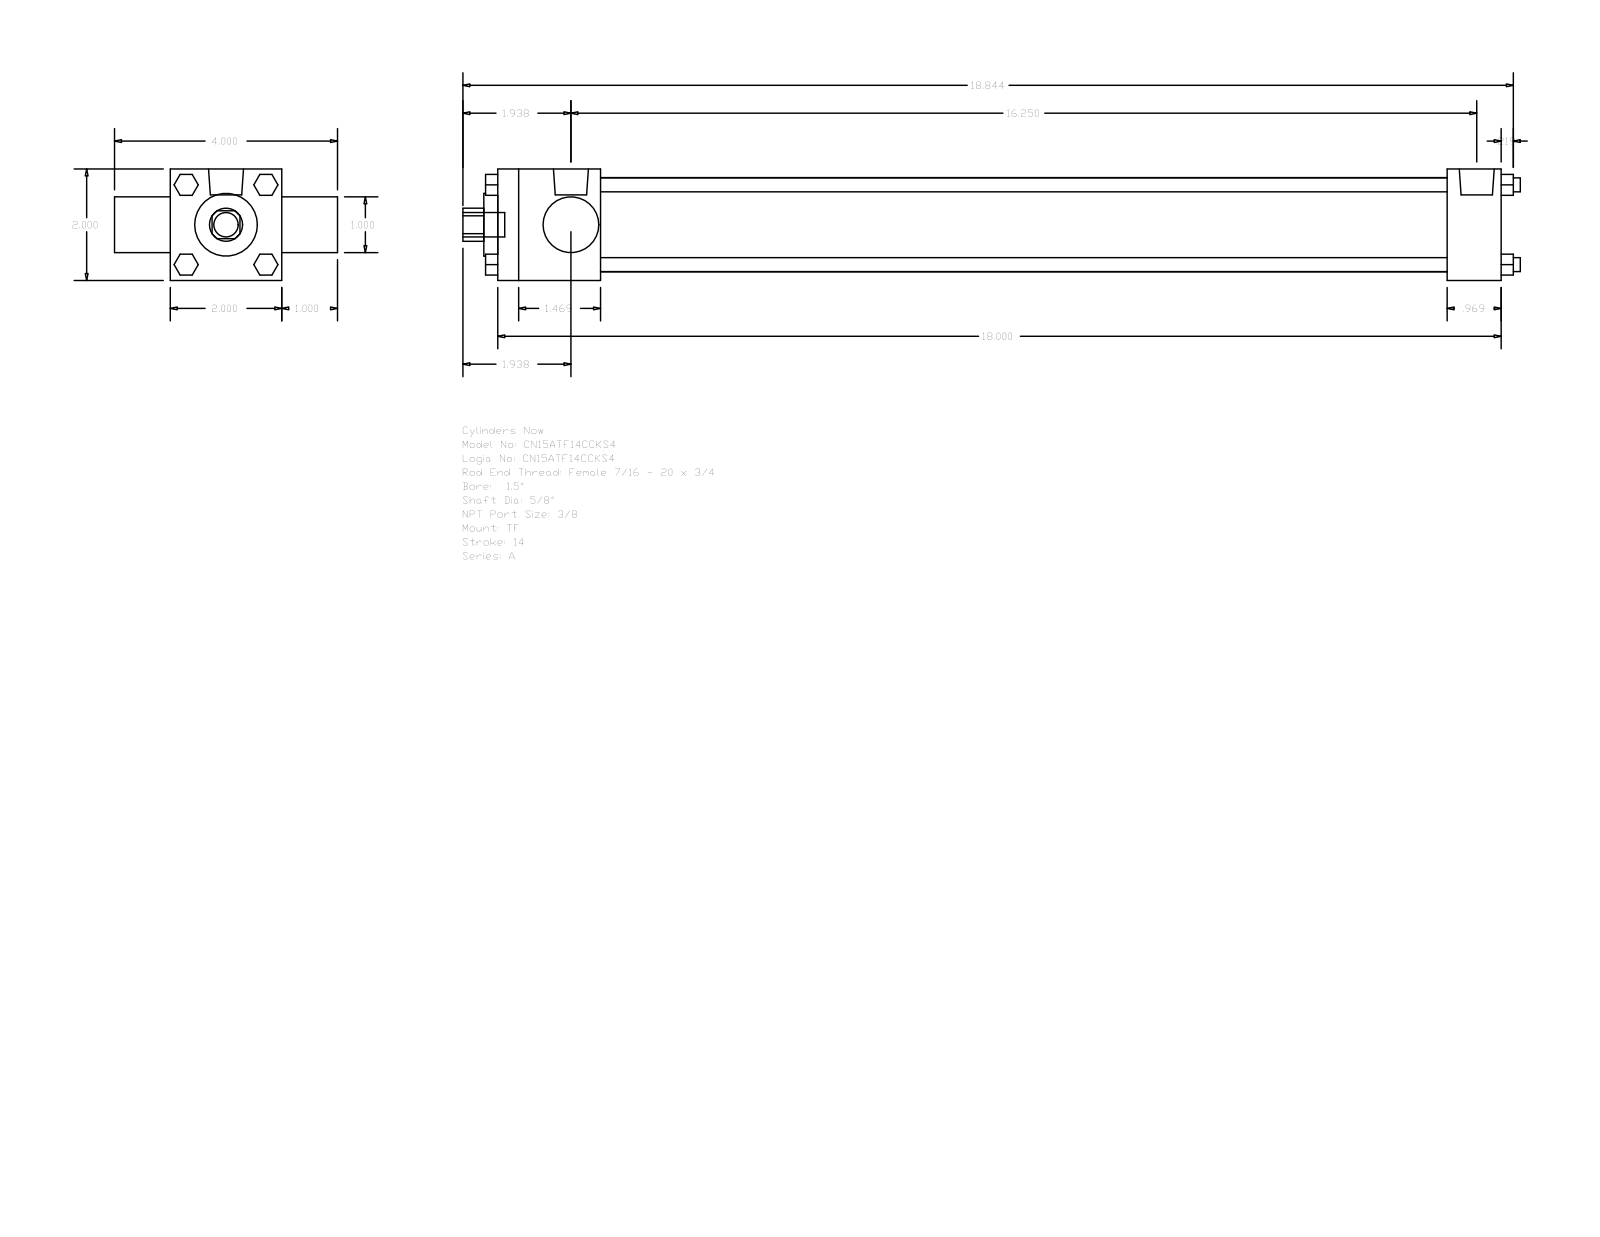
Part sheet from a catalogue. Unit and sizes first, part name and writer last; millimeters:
Units: millimetres
Overall size (bounding box): 481.81 × 101.6 × 50.8
Round holes (diameter × count): ⌀15.88 ×1, ⌀25.4 ×1, ⌀28.57 ×1, ⌀42.93 ×1
Round bosses / shafts (diameter × count): ⌀6.35 ×4, ⌀5.56 ×3, ⌀15.93 ×2, ⌀11.11 ×1
Partial cylindrical surfaces — rounded edges, fillets, slot ends (radius × count): R7.54 ×1
Main face-to-face distances: 50.8, 457.19, 25.4, 76.2, 46.83, 432.59, 385.76, 410.36, 24.6, 9.52
Bodies: 0 solids, 120 faces (92 planar, 28 cylindrical, 0 other)
Part name (STEP PRODUCT): A_TF__0150_0.625
STEP written by: GSSL Pune (CONFIG_CONTROL_DESIGN)
